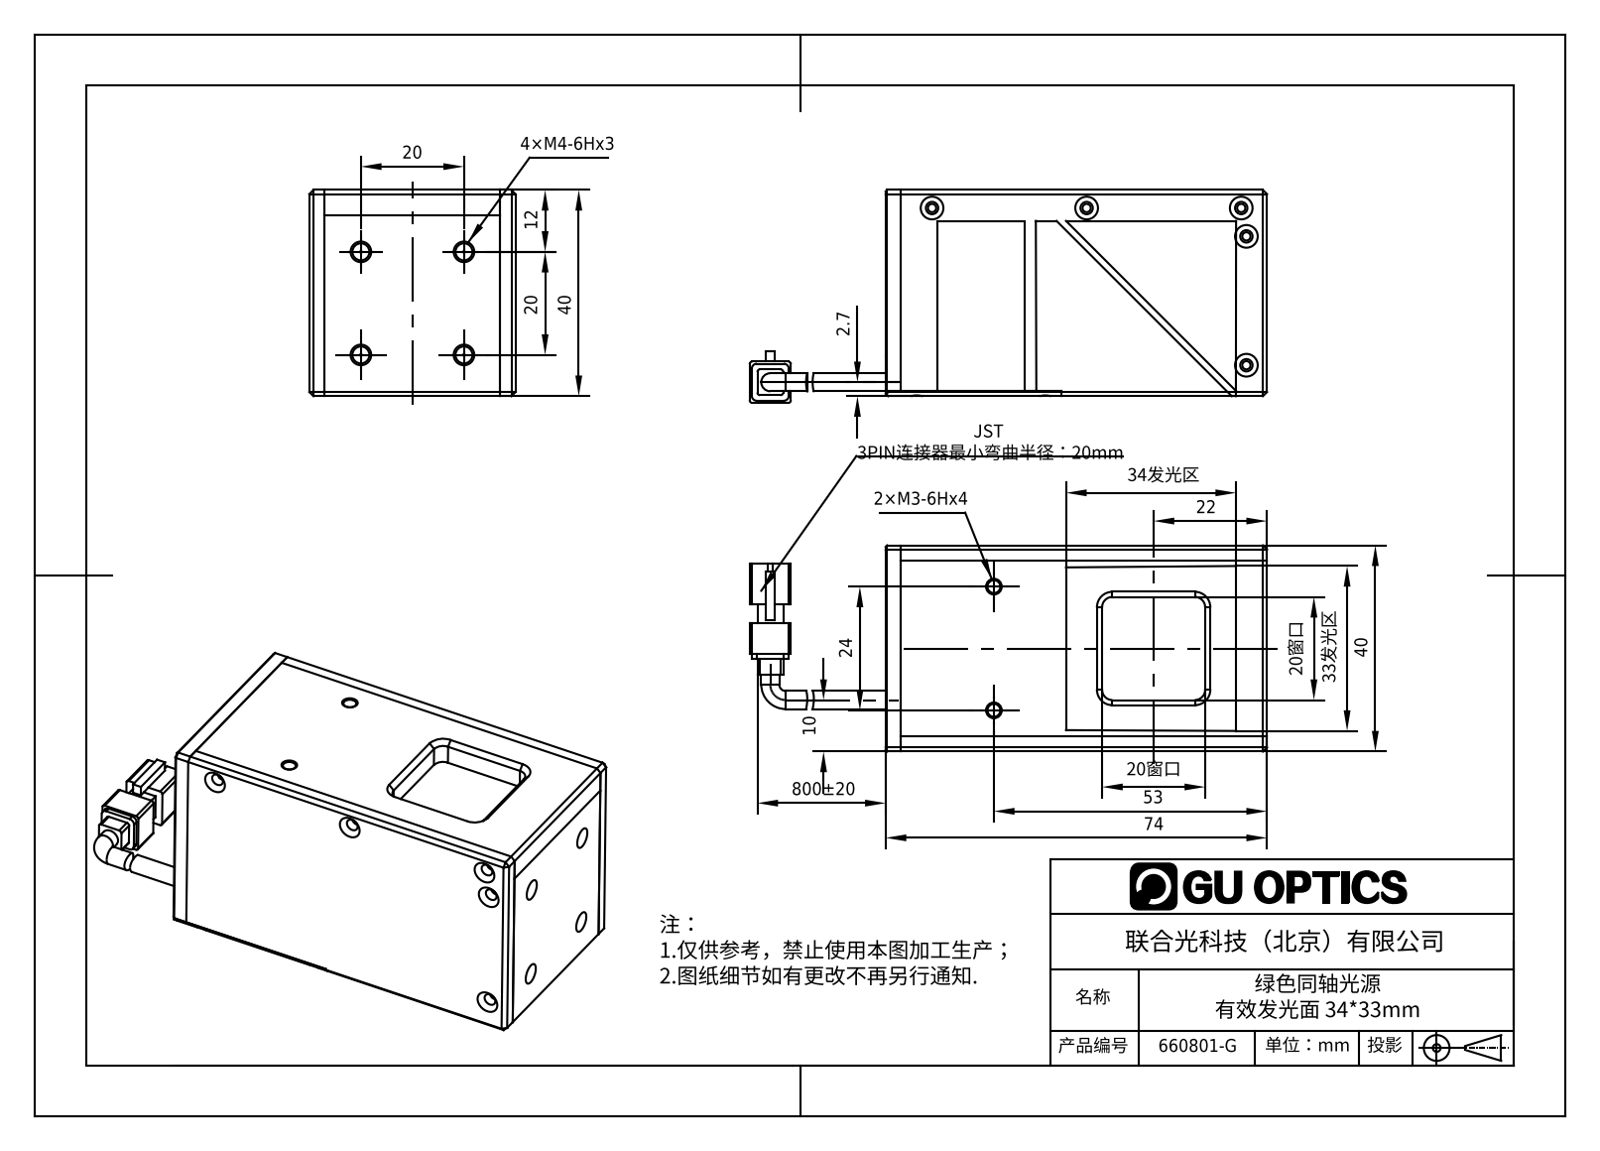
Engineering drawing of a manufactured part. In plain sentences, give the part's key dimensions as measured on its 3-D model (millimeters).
The part is named "绿色同轴光源 有效发光面 3433mm". Its 3-D file was written by "SolidWorks 2016 (AUTOMOTIVE_DESIGN)". It is 10 solids with 784 faces: 471 planar, 153 cylindrical and 160 other. Overall it measures 100.39 by 41.3 by 40 millimeters. Its volume is 48 647 cubic millimeters and its surface area 36 045 square millimeters. Round holes: 13 of diameter 1.6, 13 of diameter 2.4, 8 of diameter 4, 6 of diameter 2, 4 of diameter 3.3, 2 of diameter 2.5. Round bosses or shafts: 2 of diameter 3.5. Partial cylindrical surfaces (rounded edges, fillets, slot ends): 8 of radius 0.5, 6 of radius 0.75, 5 of radius 2, 4 of radius 1, 4 of radius 1.5, 3 of radius 1.6, 1 of radius 4. The main face-to-face distances are 1, 40, 3, 4, 36, 33, 34, 37, 6, 32. The hole center spacings are 30, 20, 25, 35, 7.5, 8.38, 11.41, 15.98.
